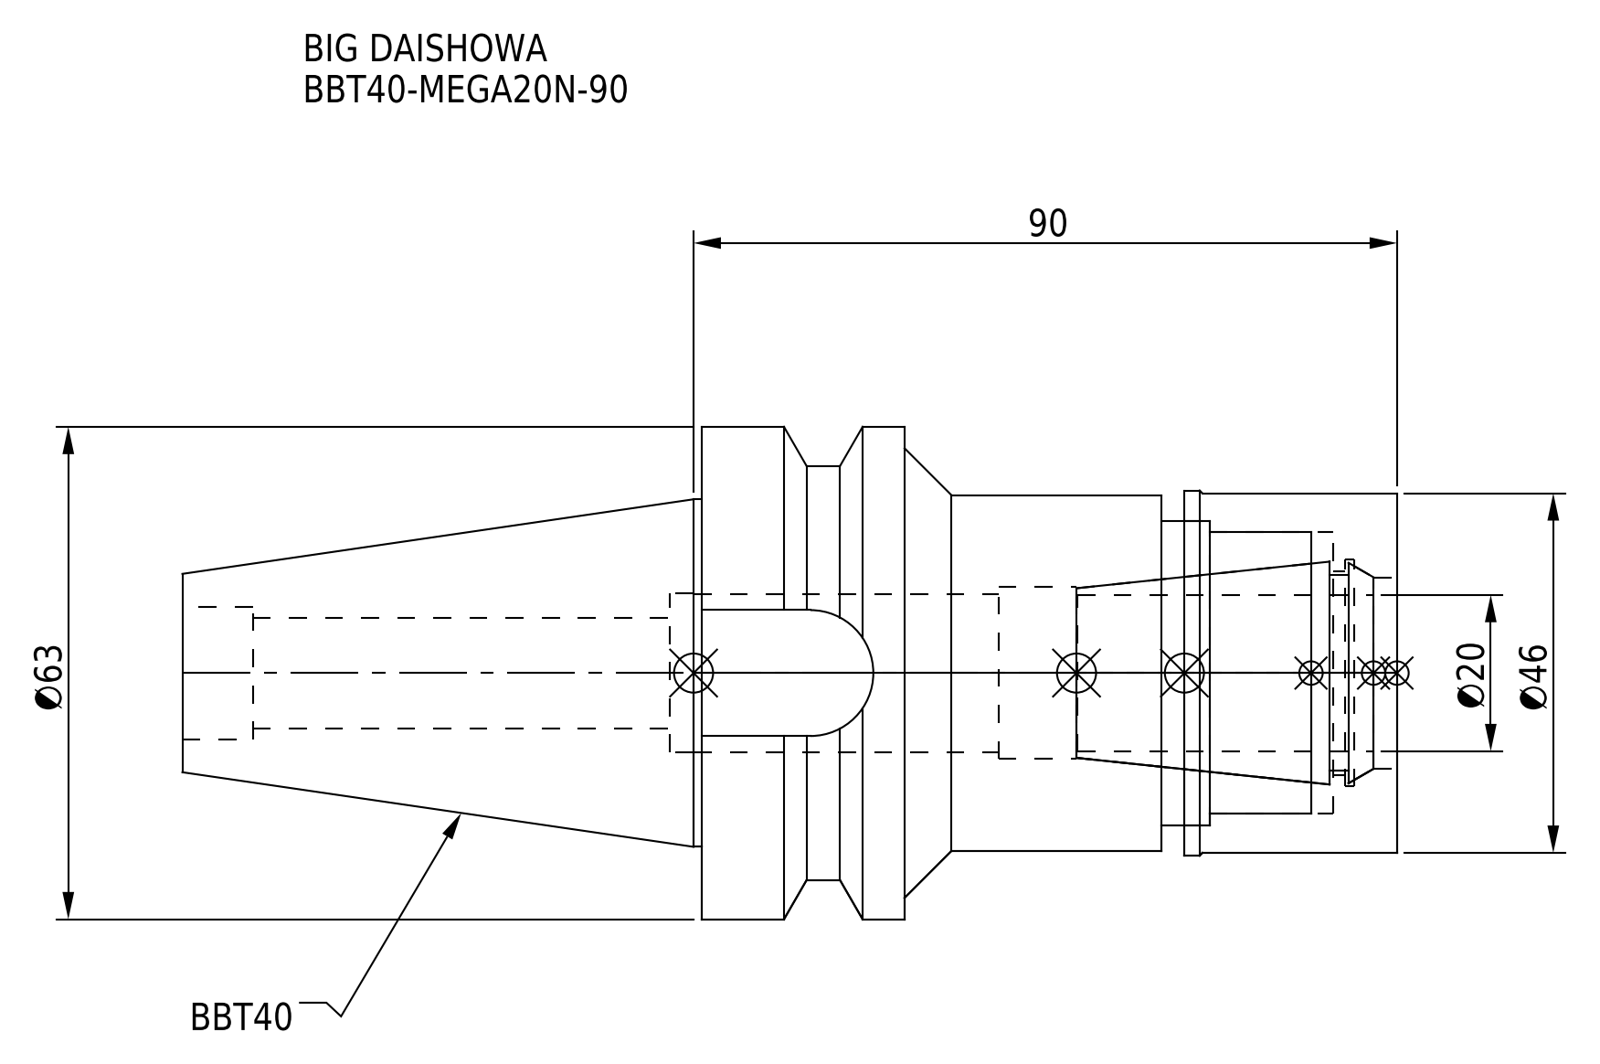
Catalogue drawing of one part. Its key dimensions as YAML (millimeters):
part_name: "BBT40-MEGA20N-90-200.stp; BBT40MN20090-200_ASM.stp; MGN20_1.stp; BBT40-MEGA20N-90 (+3 more)"
step_written_by: "SolidWorks 2019 (CONFIG_CONTROL_DESIGN)"
units: millimeters
bodies: {solids: 2, faces: 76, planar: 22, cylindrical: 40, other: 14}
overall_size: [155.4, 63, 63]
volume: 190908
surface_area: 42728
round_holes:
  - {diameter: 14.2, count: 1}
  - {diameter: 17, count: 1}
  - {diameter: 20.3, count: 1}
  - {diameter: 20.31, count: 1}
  - {diameter: 22, count: 1}
  - {diameter: 24.5, count: 1}
  - {diameter: 26, count: 1}
  - {diameter: 29, count: 1}
  - {diameter: 36, count: 1}
  - {diameter: 39, count: 1}
round_bosses_or_shafts:
  - {diameter: 63, count: 1}
  - {diameter: 53, count: 1}
  - {diameter: 46.7, count: 1}
  - {diameter: 46, count: 1}
  - {diameter: 45.5, count: 1}
  - {diameter: 44.45, count: 1}
partial_cylinders:
  - {radius: 8.05, count: 1}
face_to_face_distances: [89, 63, 26, 27.2, 35.8, 61.8, 8.2, 19, 54.8, 80.8]
